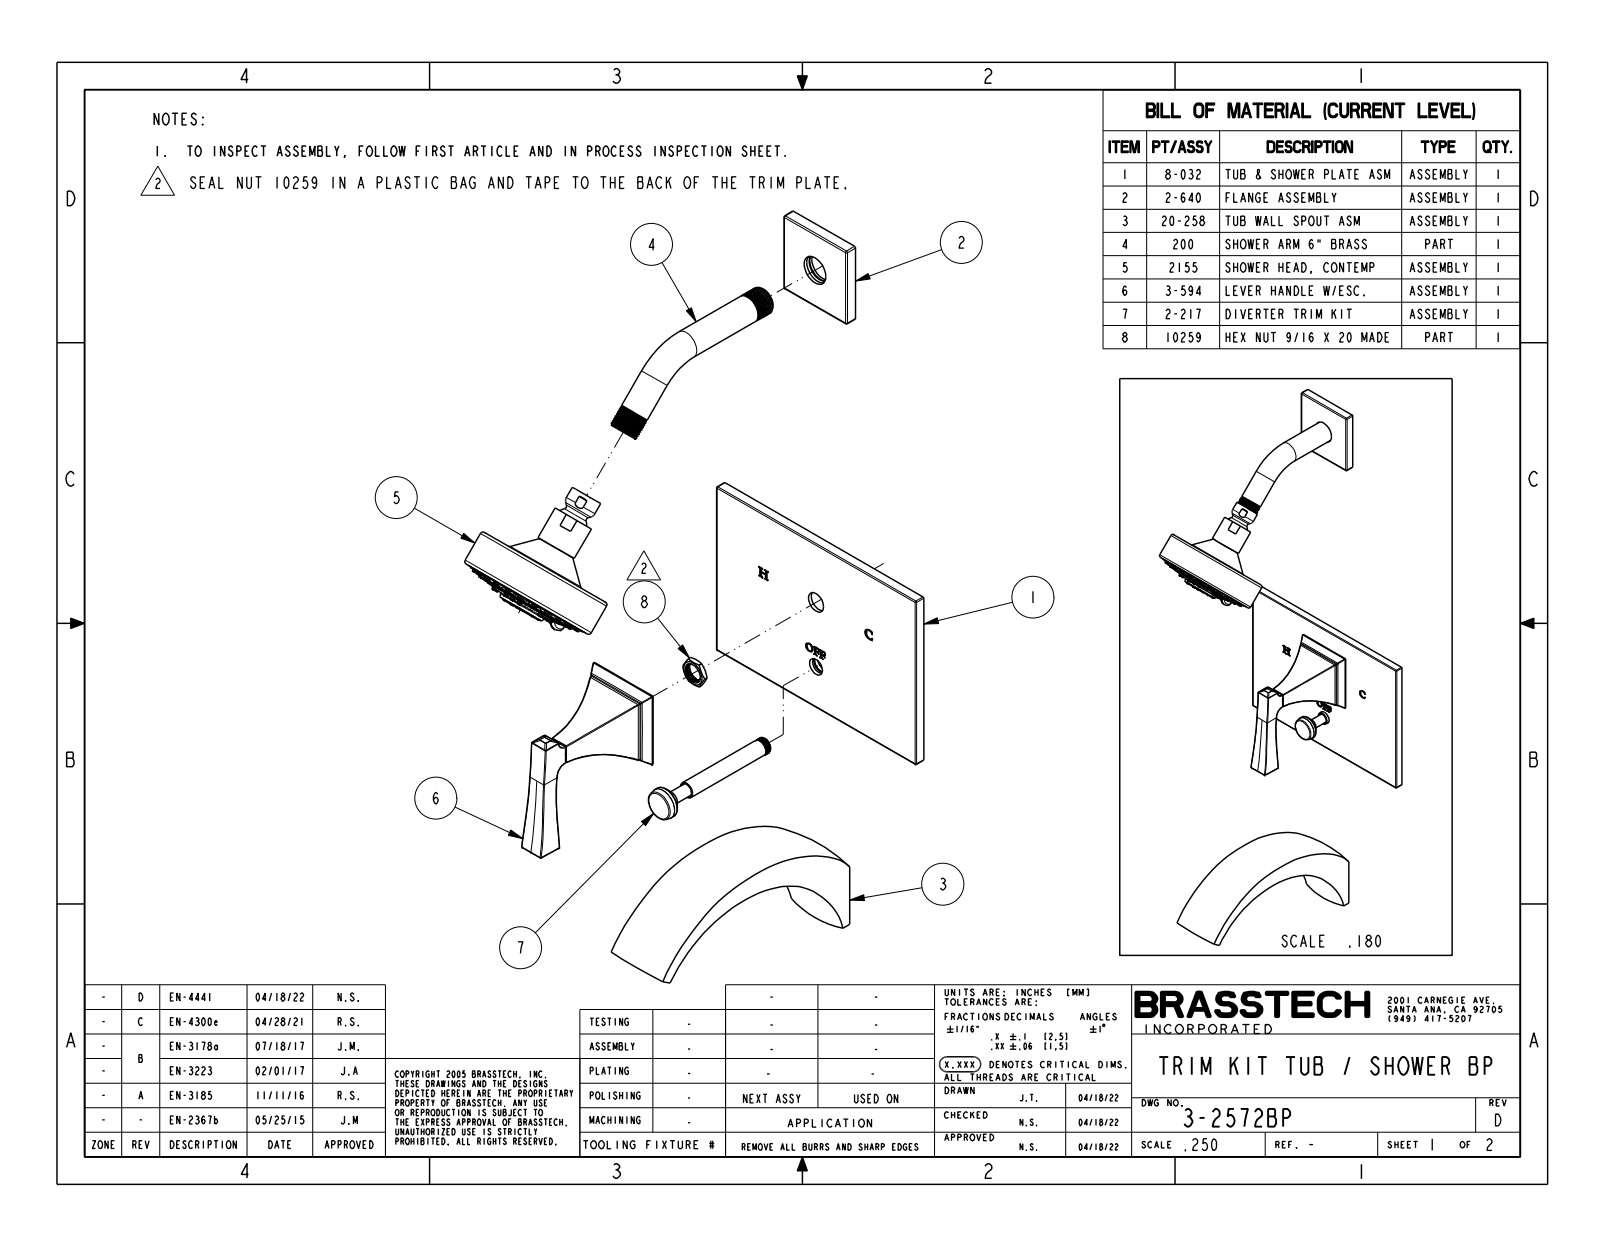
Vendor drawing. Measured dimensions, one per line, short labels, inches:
name: 3-2572BP
written by: CREO PARAMETRIC BY PTC INC, 2018400 (CONFIG_CONTROL_DESIGN)
unit: in
bodies: 3 solids, 1463 faces (202 planar, 237 cylindrical, 1024 other)
size: 23.025 × 8.175 × 7.75
volume: 55.08 in³; area: 243.2 in²
holes: 8× ⌀0.059, 1× ⌀0.925
bosses: 39× ⌀0.142, 23× ⌀0.165, 2× ⌀0.813, 1× ⌀4, 1× ⌀3.724, 1× ⌀2.323, 1× ⌀1.15, 1× ⌀0.905
rounds: 16× R0.02, 8× R0.03, 8× R0.04, 8× R0.06, 8× R0.079, 2× R0.02, 1× R0.138, 1× R0.472
face distances: 0.31, 2, 0.35, 0.04, 2.875, 4.875, 5.5, 7.75, 2.65, 5.1
hole spacings: 0.443, 0.579, 0.818, 0.819, 1.069, 0.443, 0.578, 1.069
